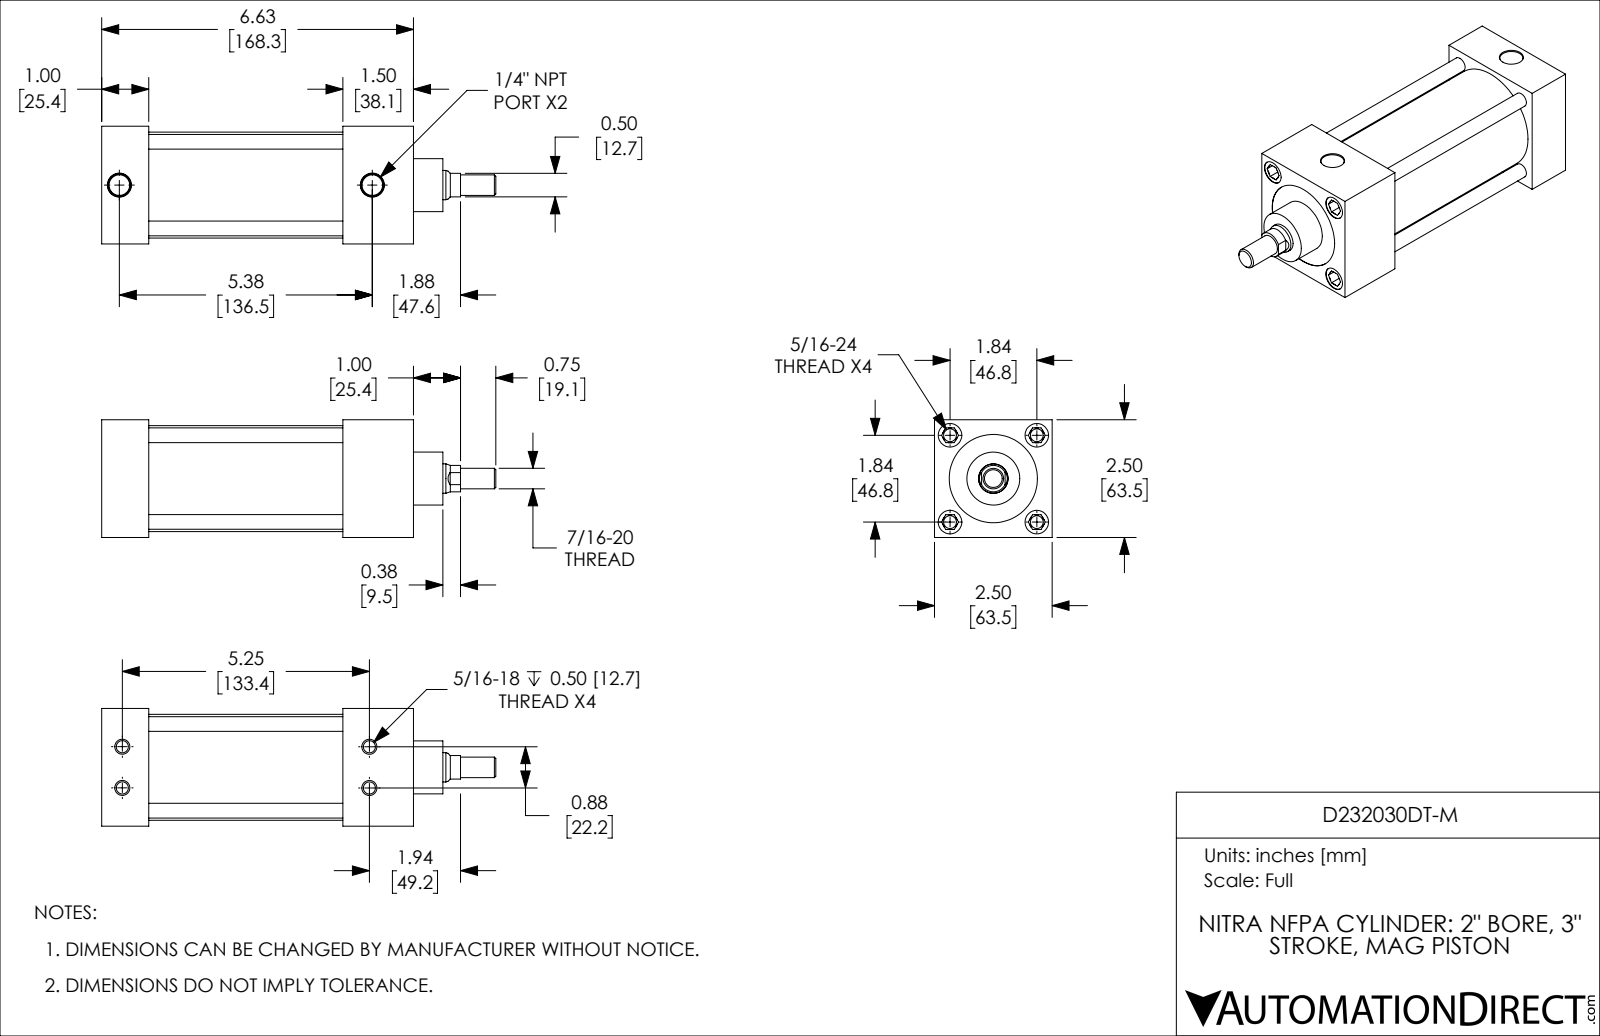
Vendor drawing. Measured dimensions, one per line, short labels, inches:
name: D232030DT-M; D232030DT-M_PISTON_KK1; D232030DT-M_BODY
written by: SolidWorks 2019 (CONFIG_CONTROL_DESIGN)
unit: in
bodies: 2 solids, 200 faces (58 planar, 62 cylindrical, 80 other)
size: 8.375 × 2.5 × 2.5
volume: 24.79 in³; area: 159.6 in²
holes: 7× ⌀0.272, 4× ⌀0.257, 4× ⌀0.5, 2× ⌀0.438, 1× ⌀0.626, 1× ⌀1.875, 1× ⌀2.001
bosses: 4× ⌀0.312, 1× ⌀2.251, 1× ⌀1.999, 1× ⌀1.125, 1× ⌀0.624, 1× ⌀0.437
rounds: 1× R0.281
face distances: 2.5, 1, 5.125, 4.125, 1.125, 2.125, 3, 1.5, 6.625, 5.625
hole spacings: 1.84, 1.844, 1.301, 0.441, 0.443, 0.875, 1.304, 2.602
